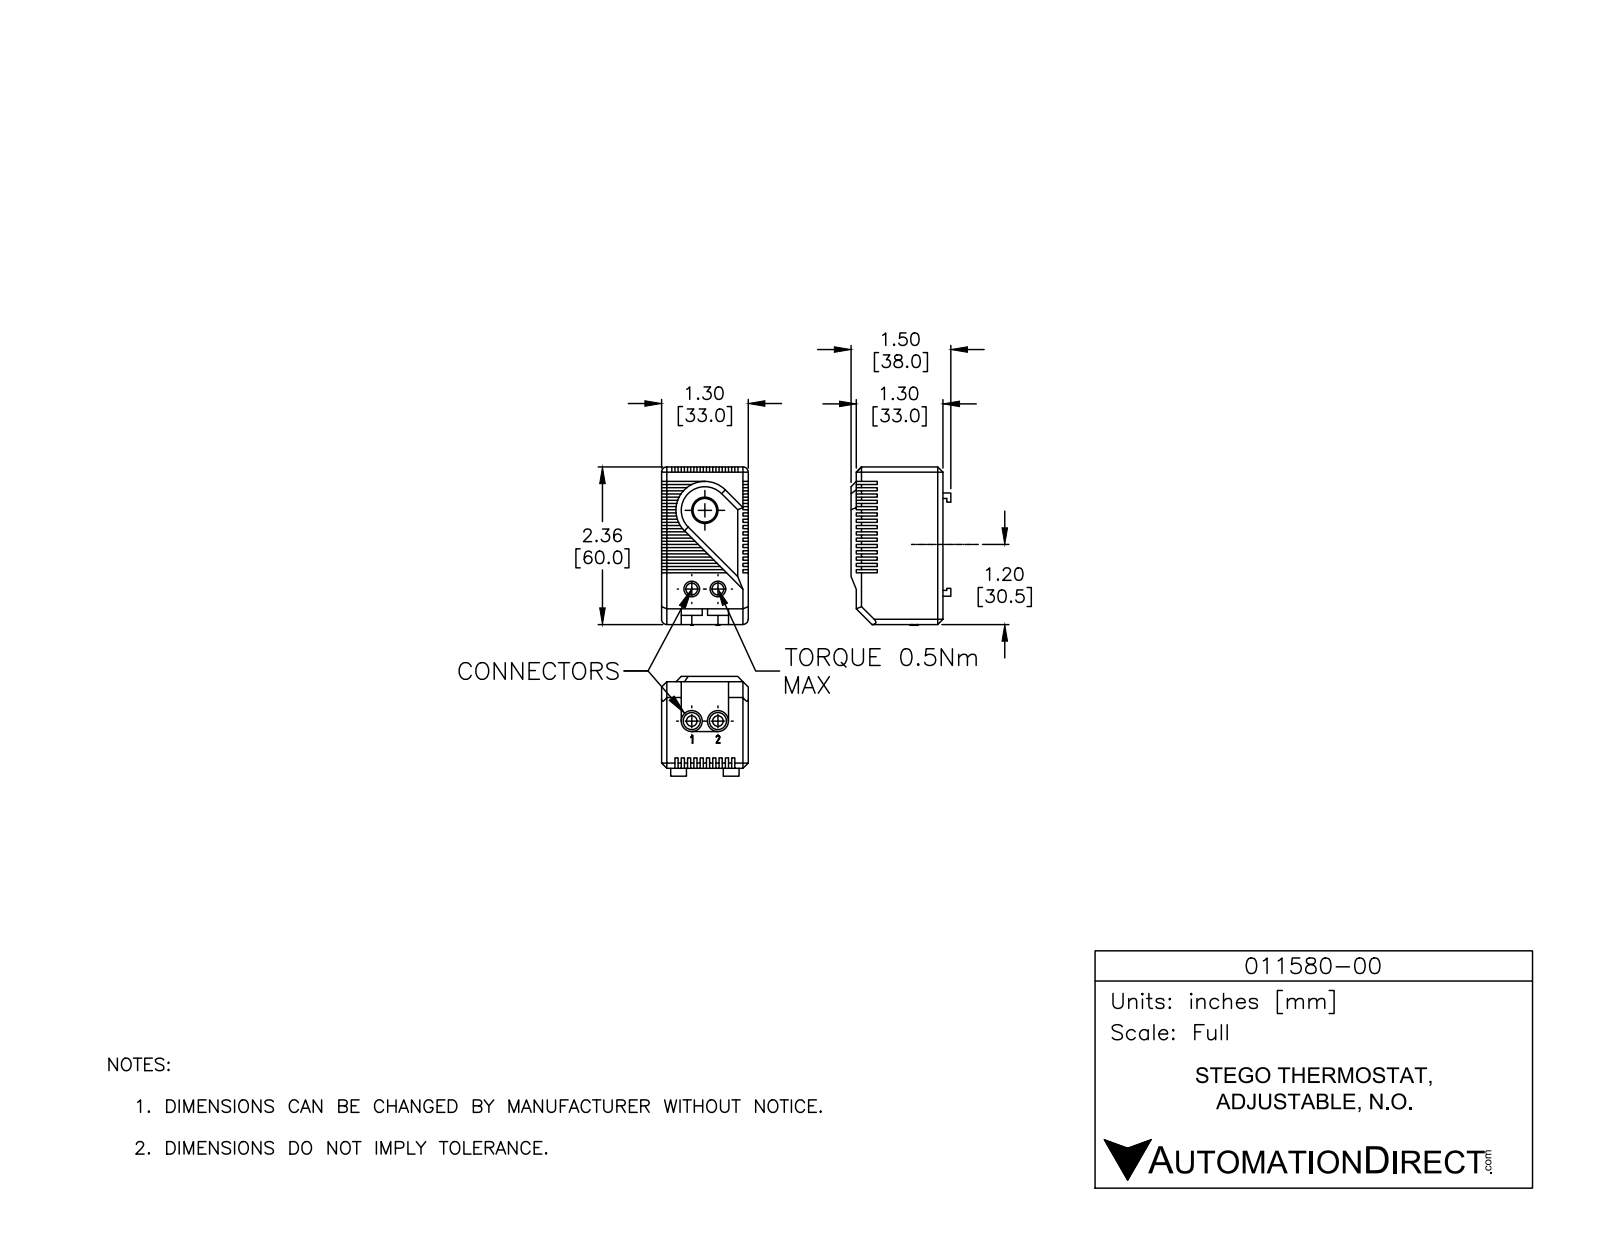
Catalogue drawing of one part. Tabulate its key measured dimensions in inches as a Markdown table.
| quantity | value |
| --- | --- |
| part name | 011580-00 |
| STEP written by | SolidWorks 2017 (AUTOMOTIVE_DESIGN) |
| units | inches |
| bodies | 2 solids, 662 faces (538 planar, 40 cylindrical, 84 other) |
| overall size | 2.374 × 1.496 × 1.317 |
| volume | 3.757 in³ |
| surface area | 21.36 in² |
| round holes (diameter × count) | 0.157 × 2, 0.177 × 2, 0.236 × 2, 0.256 × 2, 0.394 × 1 |
| round bosses / shafts (diameter × count) | 0.315 × 2, 0.37 × 1 |
| partial cylindrical surfaces (radius × count) | 0.079 × 4, 0.054 × 1, 0.06 × 1, 0.433 × 1 |
| main face-to-face distances | 1.299, 0.094, 0.047, 0.189, 0.236, 0.142, 0.079, 0.283, 0.378, 0.331 |
| hole center spacings | 0.394, 1.197 |
